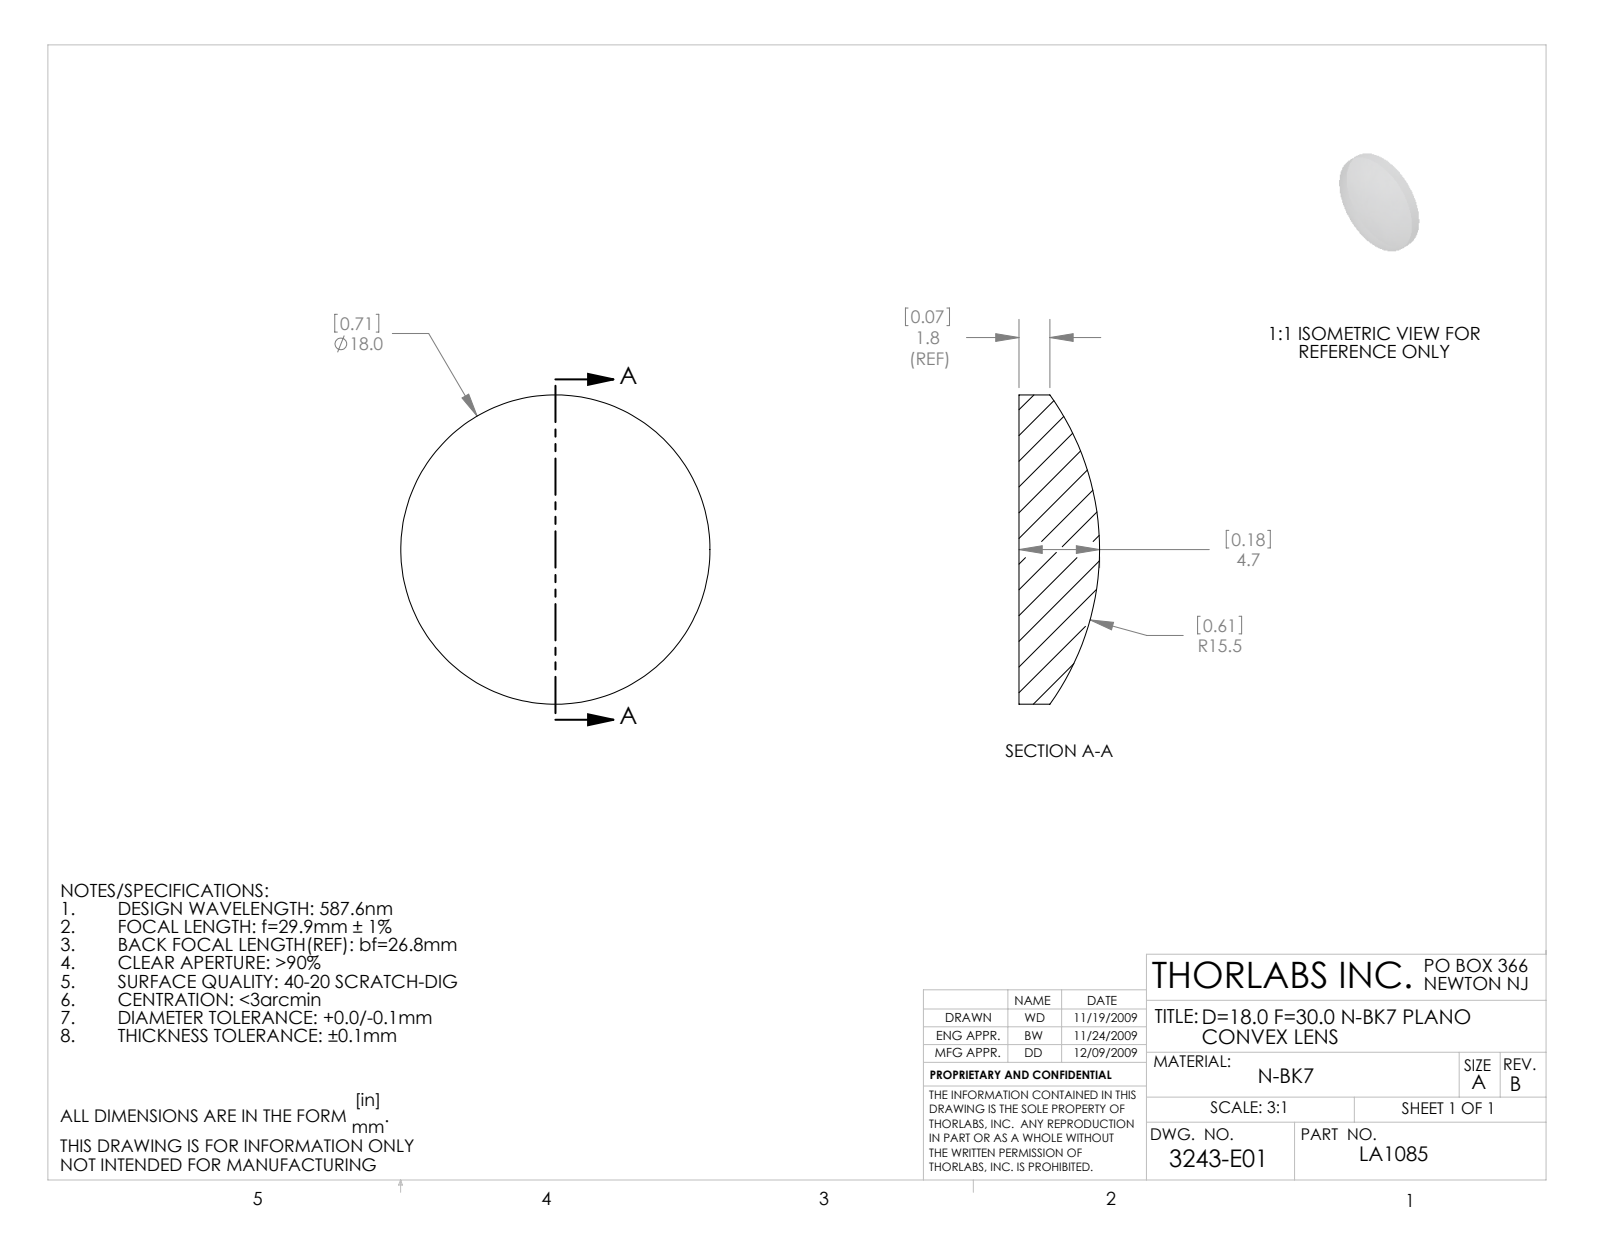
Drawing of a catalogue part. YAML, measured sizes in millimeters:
part_name: "3243-E0W"
step_written_by: "SolidWorks 2009 (AUTOMOTIVE_DESIGN)"
units: millimeters
bodies: {solids: 1, faces: 5, planar: 1, cylindrical: 2, other: 2}
overall_size: [18, 18, 4.69]
volume: 838
surface_area: 637
round_bosses_or_shafts:
  - {diameter: 18, count: 1}
